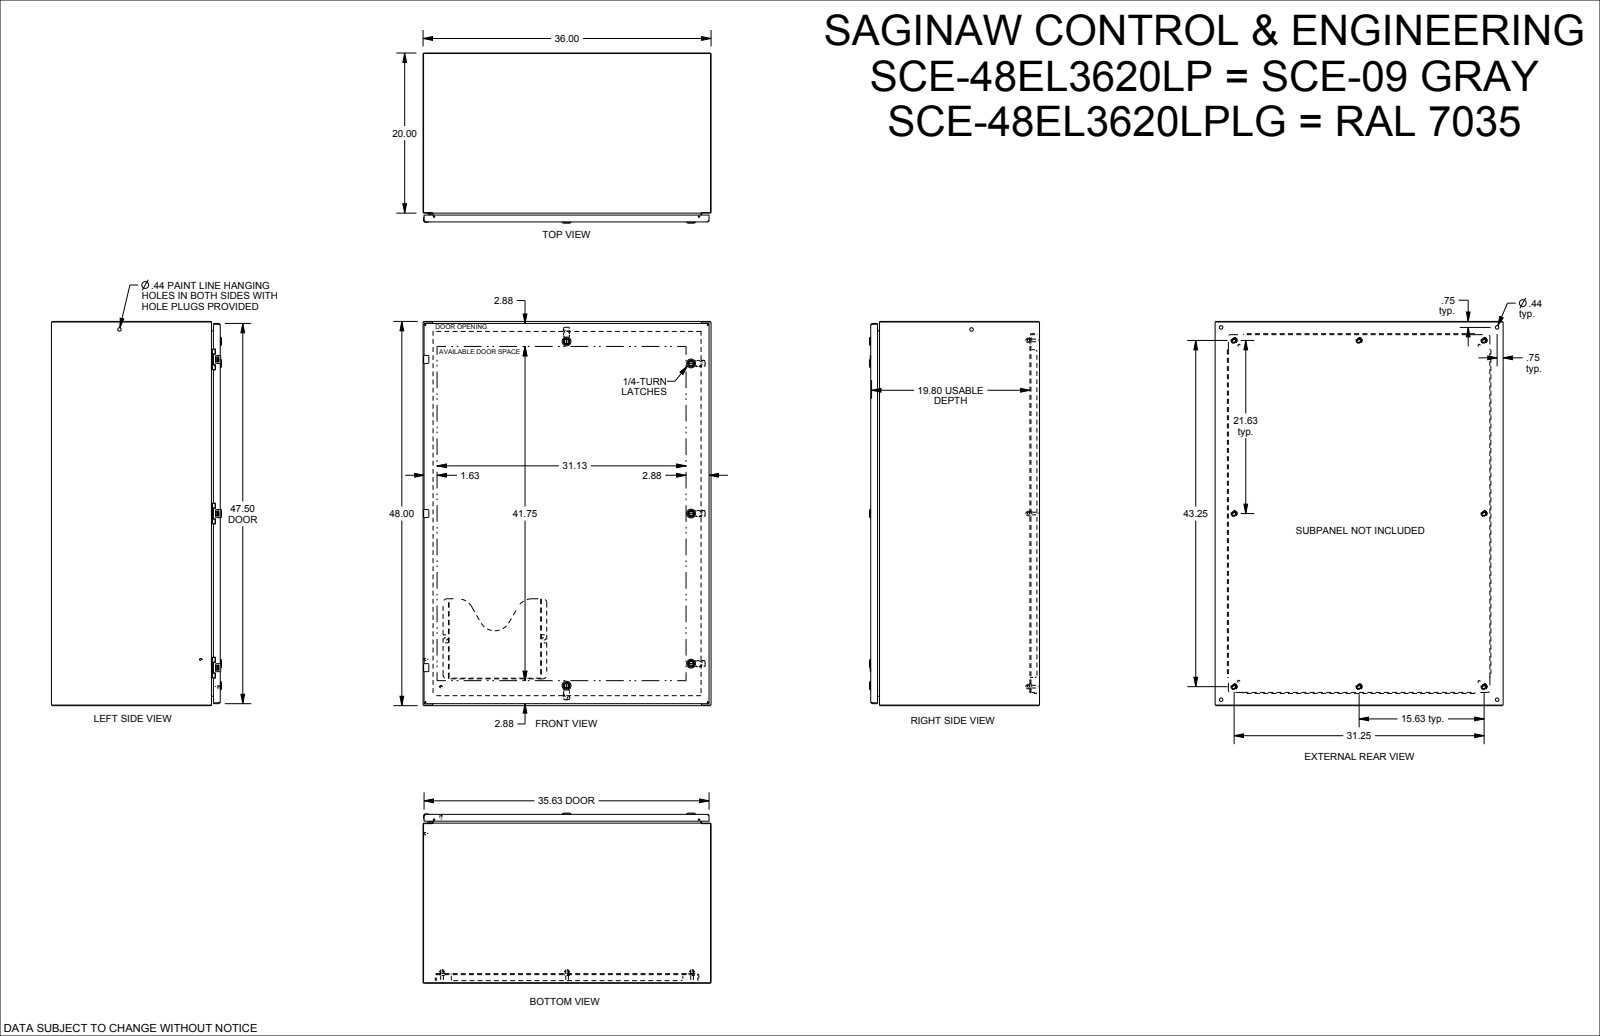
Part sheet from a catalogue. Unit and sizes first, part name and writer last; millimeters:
Units: millimetres
Overall size (bounding box): 1219.2 × 914.4 × 539.9
Round holes (diameter × count): ⌀9.3 ×8, ⌀12.7 ×8, ⌀4.4 ×6, ⌀5.2 ×6, ⌀6.2 ×6, ⌀6.8 ×6, ⌀9.5 ×6, ⌀5 ×5, ⌀8 ×5, ⌀10 ×5, ⌀11.1 ×5, ⌀16.1 ×5
Round bosses / shafts (diameter × count): ⌀4.3 ×9, ⌀9.3 ×8, ⌀8.4 ×8, ⌀6.4 ×6, ⌀6.1 ×6, ⌀28 ×5, ⌀22 ×5, ⌀20.4 ×5
Partial cylindrical surfaces — rounded edges, fillets, slot ends (radius × count): R0.3 ×136, R0.3 ×52, R0.5 ×52, R0.4 ×32, R4 ×20, R1 ×17, R0.6 ×16, R2.5 ×16
Main face-to-face distances: 1.9, 1.9, 912.5, 2.6, 531.4, 533.3, 535.9, 534, 28.6, 502.8
Hole centre spacings: 489, 977.9, 1.3, 12.5, 12.5, 25, 463.9, 476.4
Bodies: 0 solids, 4770 faces (2330 planar, 1321 cylindrical, 1119 other)
Part name (STEP PRODUCT): SCE-48EL3620LP
STEP written by: SolidWorks 2019 (CONFIG_CONTROL_DESIGN)
